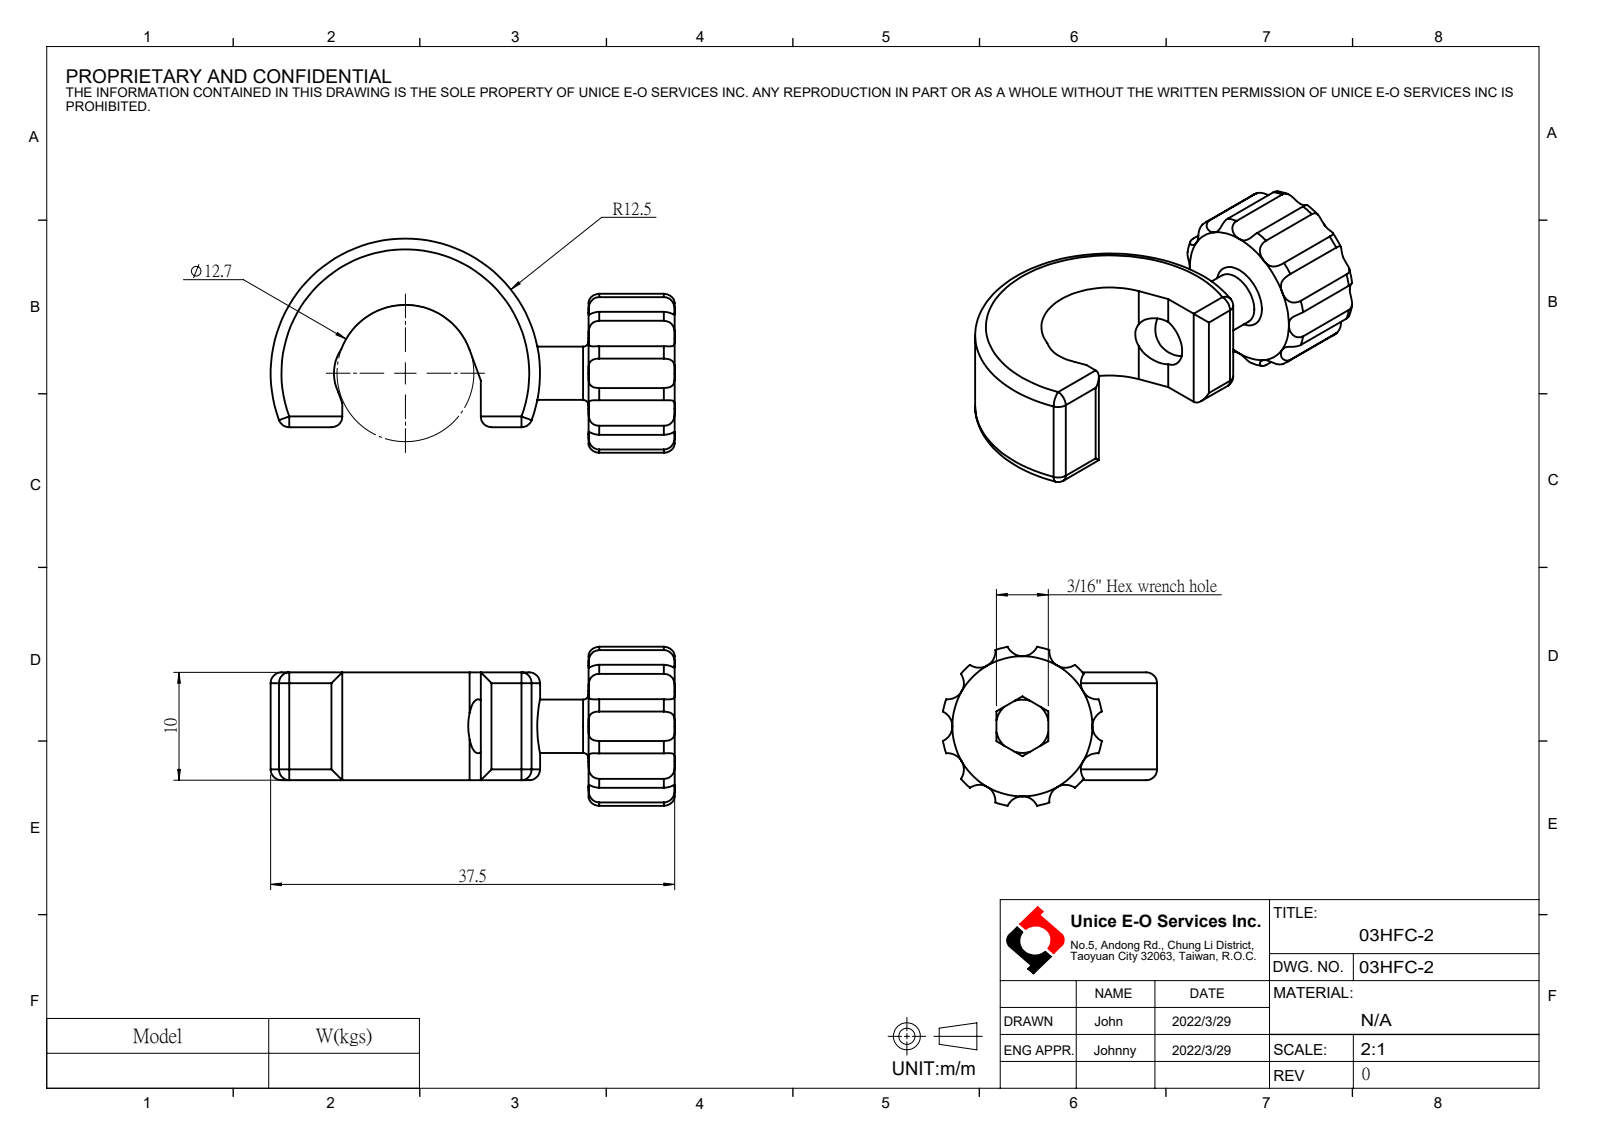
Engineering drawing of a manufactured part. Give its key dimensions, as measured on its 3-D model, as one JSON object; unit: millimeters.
{"part_name": "03HFC-2", "step_written_by": "SolidWorks 2021 (CONFIG_CONTROL_DESIGN)", "units": "millimeters", "bodies": {"solids": 0, "faces": 101, "planar": 17, "cylindrical": 46, "other": 38}, "overall_size": [37.5, 19.88, 14.75], "round_holes": [[5, 1]], "round_bosses_or_shafts": [[4.94, 1]], "partial_cylinders_radius": [[1.5, 12], [1, 6], [4, 1], [6.35, 1], [7.5, 1], [12.5, 1]], "face_to_face_distances": [10, 8, 18, 4.8, 30.85, 22.85, 12.85, 12.8, 2.6, 7.41]}
